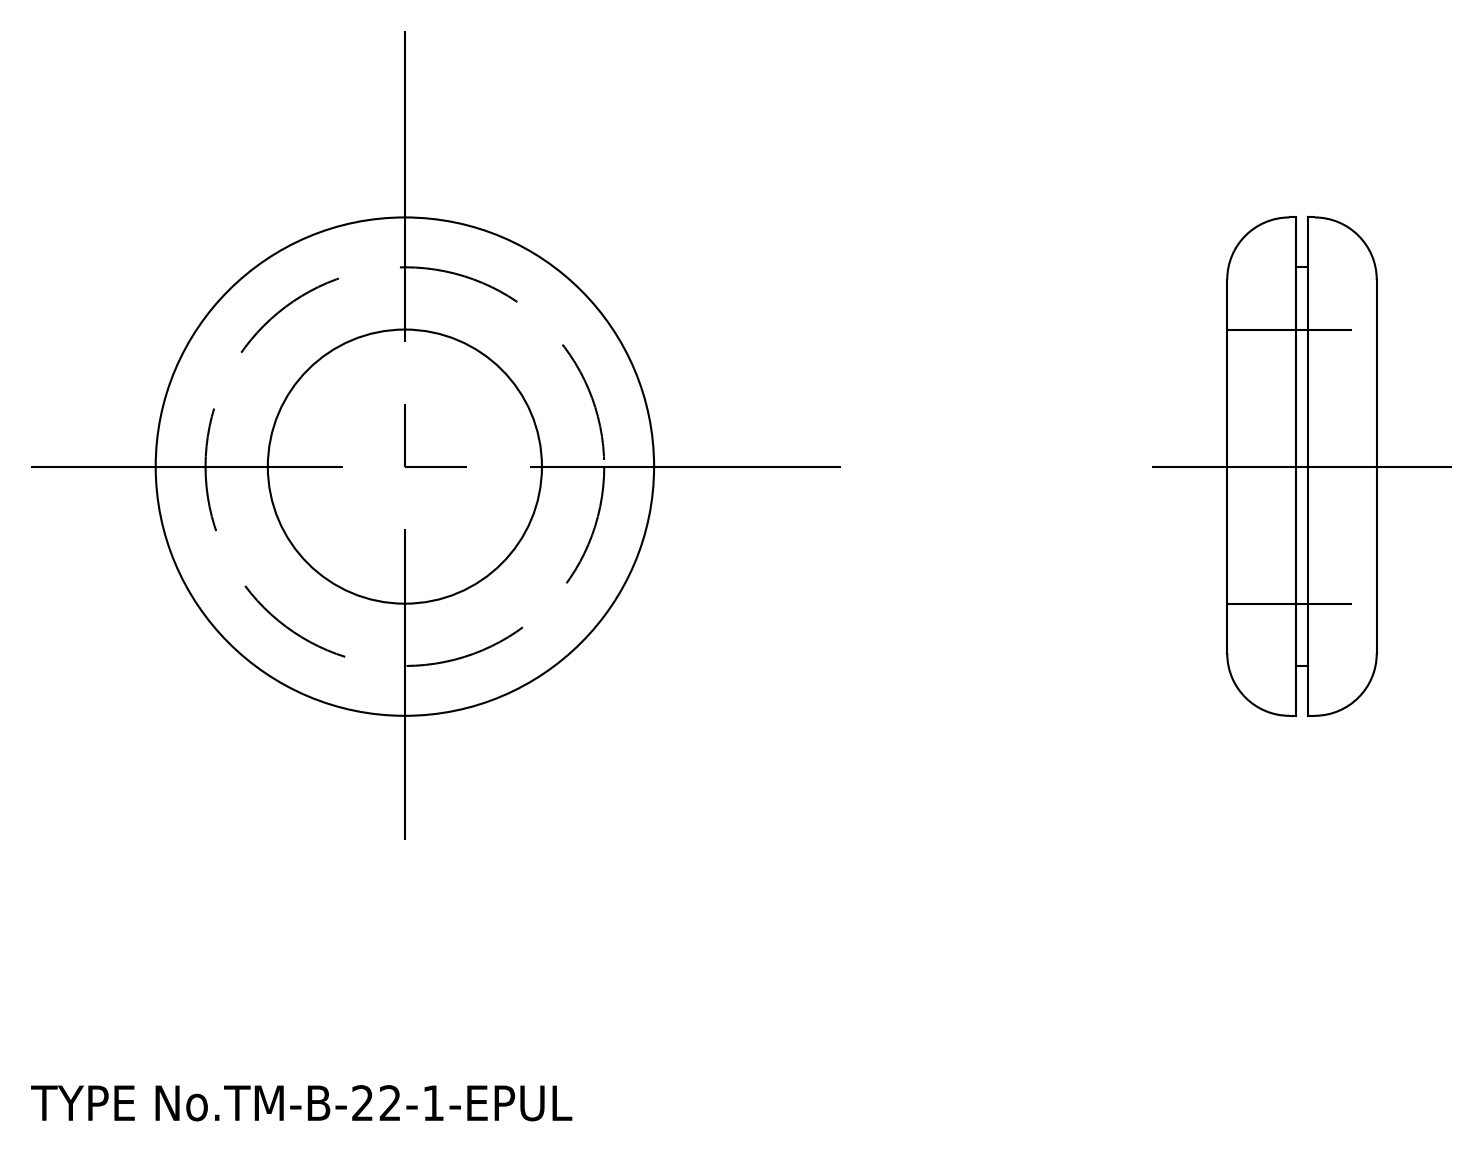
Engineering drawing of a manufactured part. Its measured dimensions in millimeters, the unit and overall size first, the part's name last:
Units: millimetres
Overall size (bounding box): 40 × 40 × 12
Round holes (diameter × count): ⌀22 ×1
Round bosses / shafts (diameter × count): ⌀40 ×1, ⌀32 ×1
Main face-to-face distances: 5.5, 6.5, 1, 12
Volume: 8 799 mm³ · Surface area: 4 411 mm²
Bodies: 1 solid, 16 faces (4 planar, 8 cylindrical, 4 other)
STEP written by: spGate 15.6.1 (AUTOMOTIVE_DESIGN)
